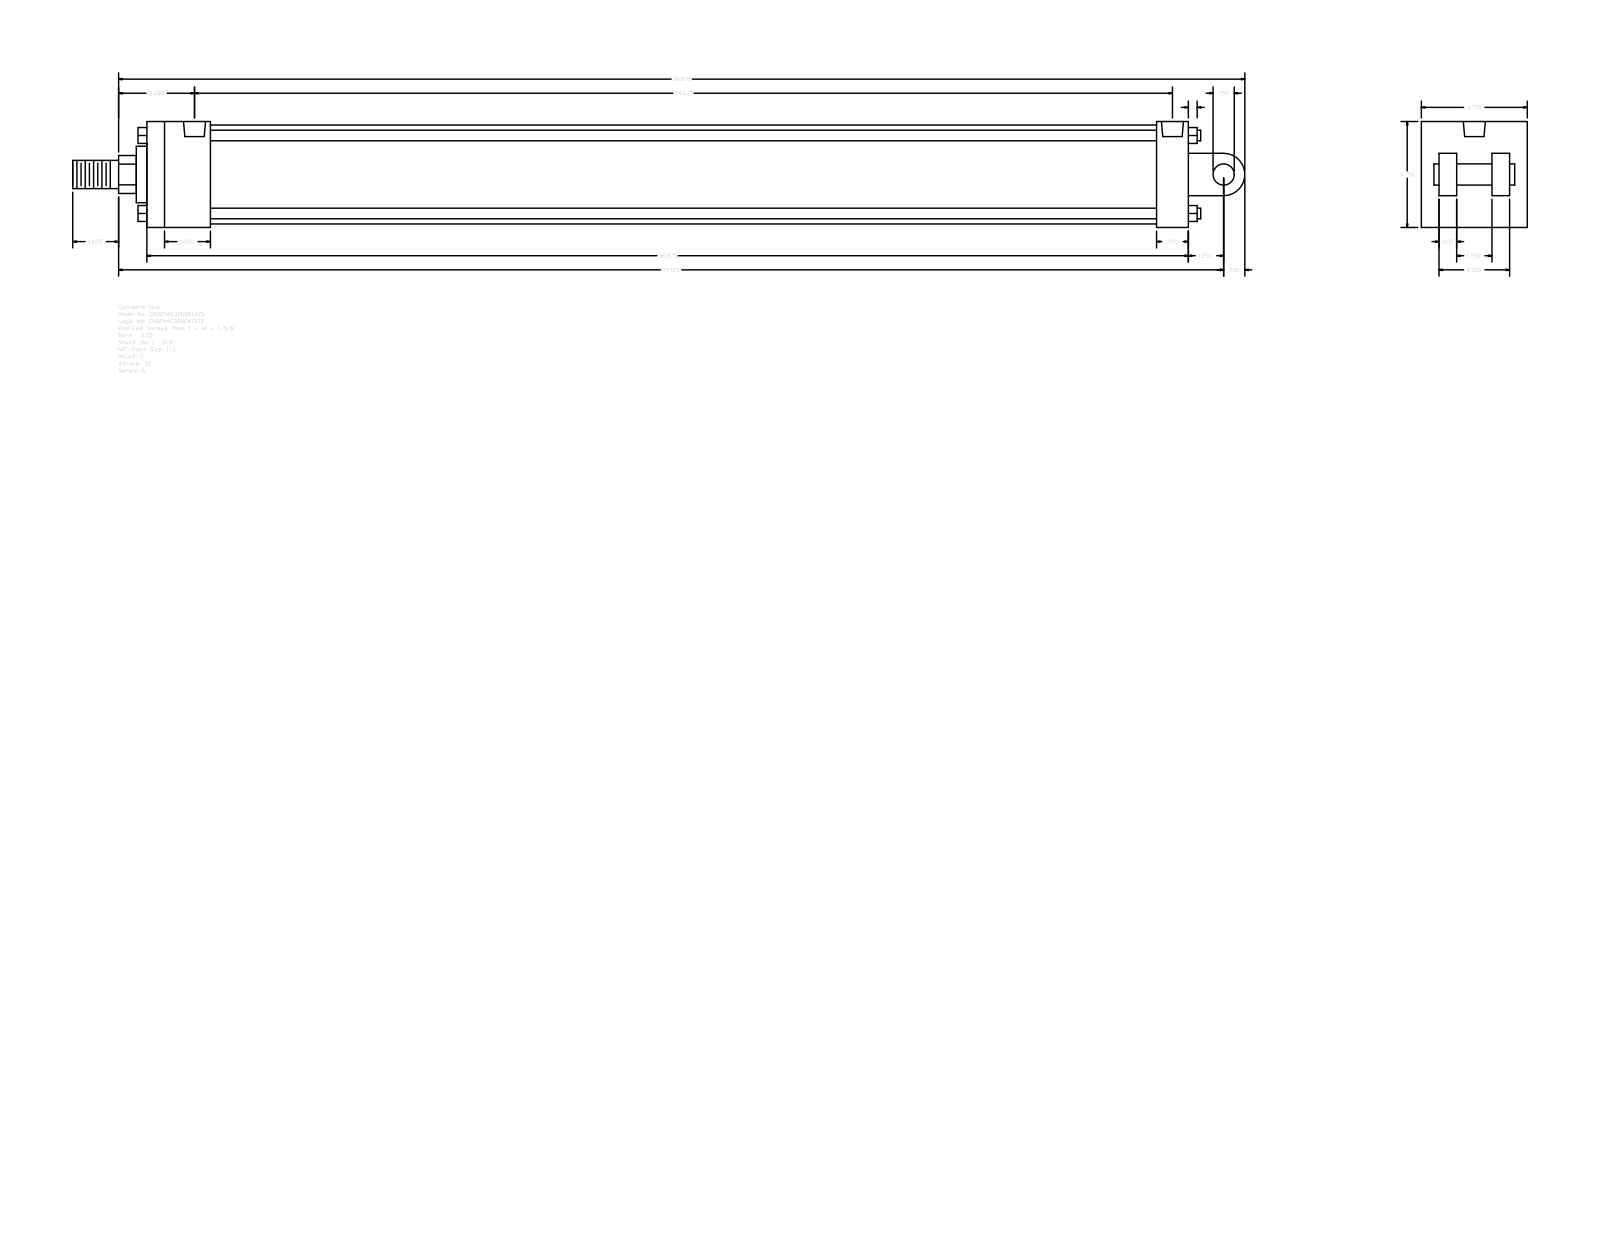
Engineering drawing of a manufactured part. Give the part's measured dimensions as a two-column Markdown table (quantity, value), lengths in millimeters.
| quantity | value |
| --- | --- |
| part name | A_C__0325_1.375 |
| STEP written by | GSSL Pune (CONFIG_CONTROL_DESIGN) |
| units | millimeters |
| bodies | 0 solids, 135 faces (102 planar, 33 cylindrical, 0 other) |
| overall size | 1054.1 × 95.25 × 95.25 |
| round holes (diameter × count) | 8.73 × 4, 19.77 × 2 |
| round bosses / shafts (diameter × count) | 9.53 × 4, 88.9 × 1, 50.8 × 1, 34.92 × 1, 25.4 × 1, 19.05 × 1 |
| partial cylindrical surfaces (radius × count) | 17.06 × 1, 19.05 × 1 |
| main face-to-face distances | 95.24, 936.62, 15.87, 28.57, 63.5, 66.67, 57.15, 31.74, 79.37, 47.63 |
| hole center spacings | 3.18, 873.12, 876.3, 879.48 |
